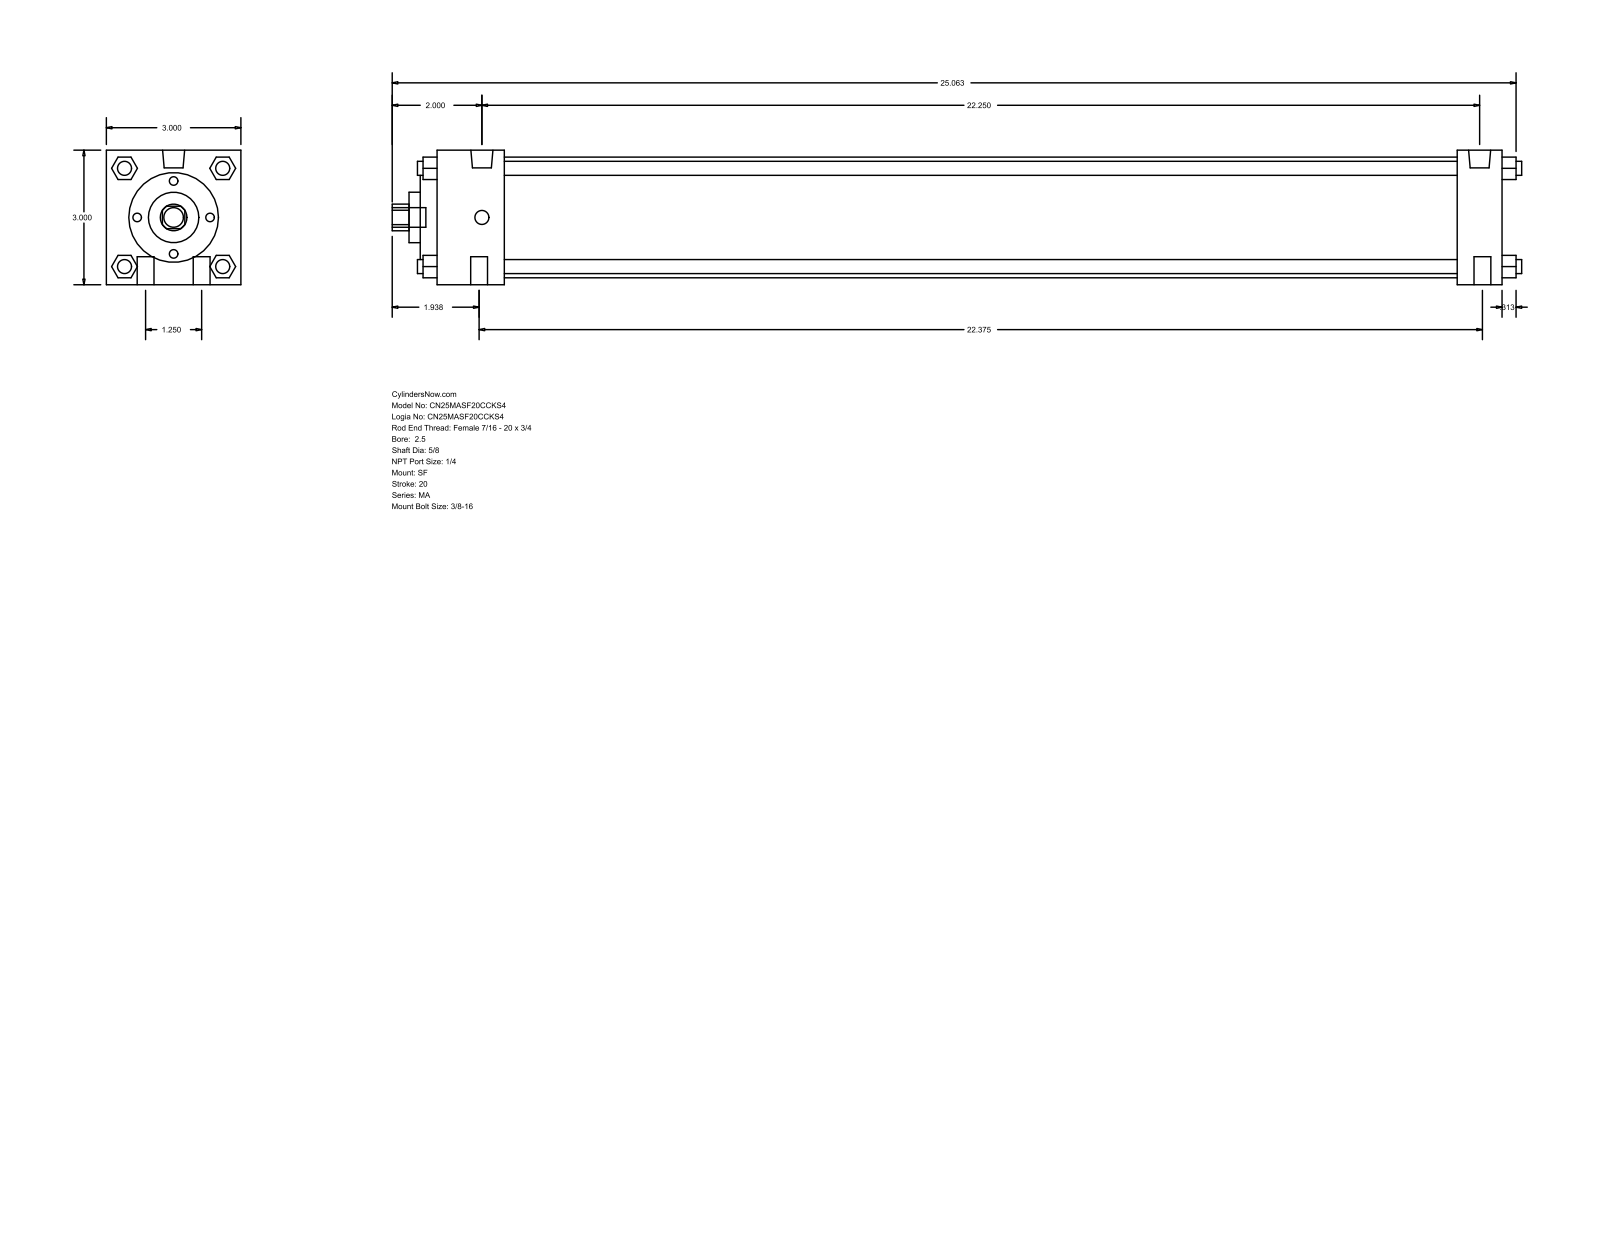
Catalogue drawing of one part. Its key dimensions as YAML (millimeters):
part_name: "MA_SF__0250_0.625"
step_written_by: "GSSL Pune (CONFIG_CONTROL_DESIGN)"
units: millimeters
bodies: {solids: 0, faces: 126, planar: 95, cylindrical: 31, other: 0}
overall_size: [639.76, 76.2, 76.2]
round_holes:
  - {diameter: 15.88, count: 1}
  - {diameter: 28.57, count: 1}
  - {diameter: 50.8, count: 1}
  - {diameter: 68.33, count: 1}
round_bosses_or_shafts:
  - {diameter: 7.94, count: 6}
  - {diameter: 9.53, count: 4}
  - {diameter: 12.49, count: 2}
  - {diameter: 11.11, count: 1}
partial_cylinders:
  - {radius: 7.54, count: 1}
face_to_face_distances: [76.2, 603.25, 25.4, 577.85, 38.1, 539.75, 565.15, 12.7, 9.52, 47.62]
